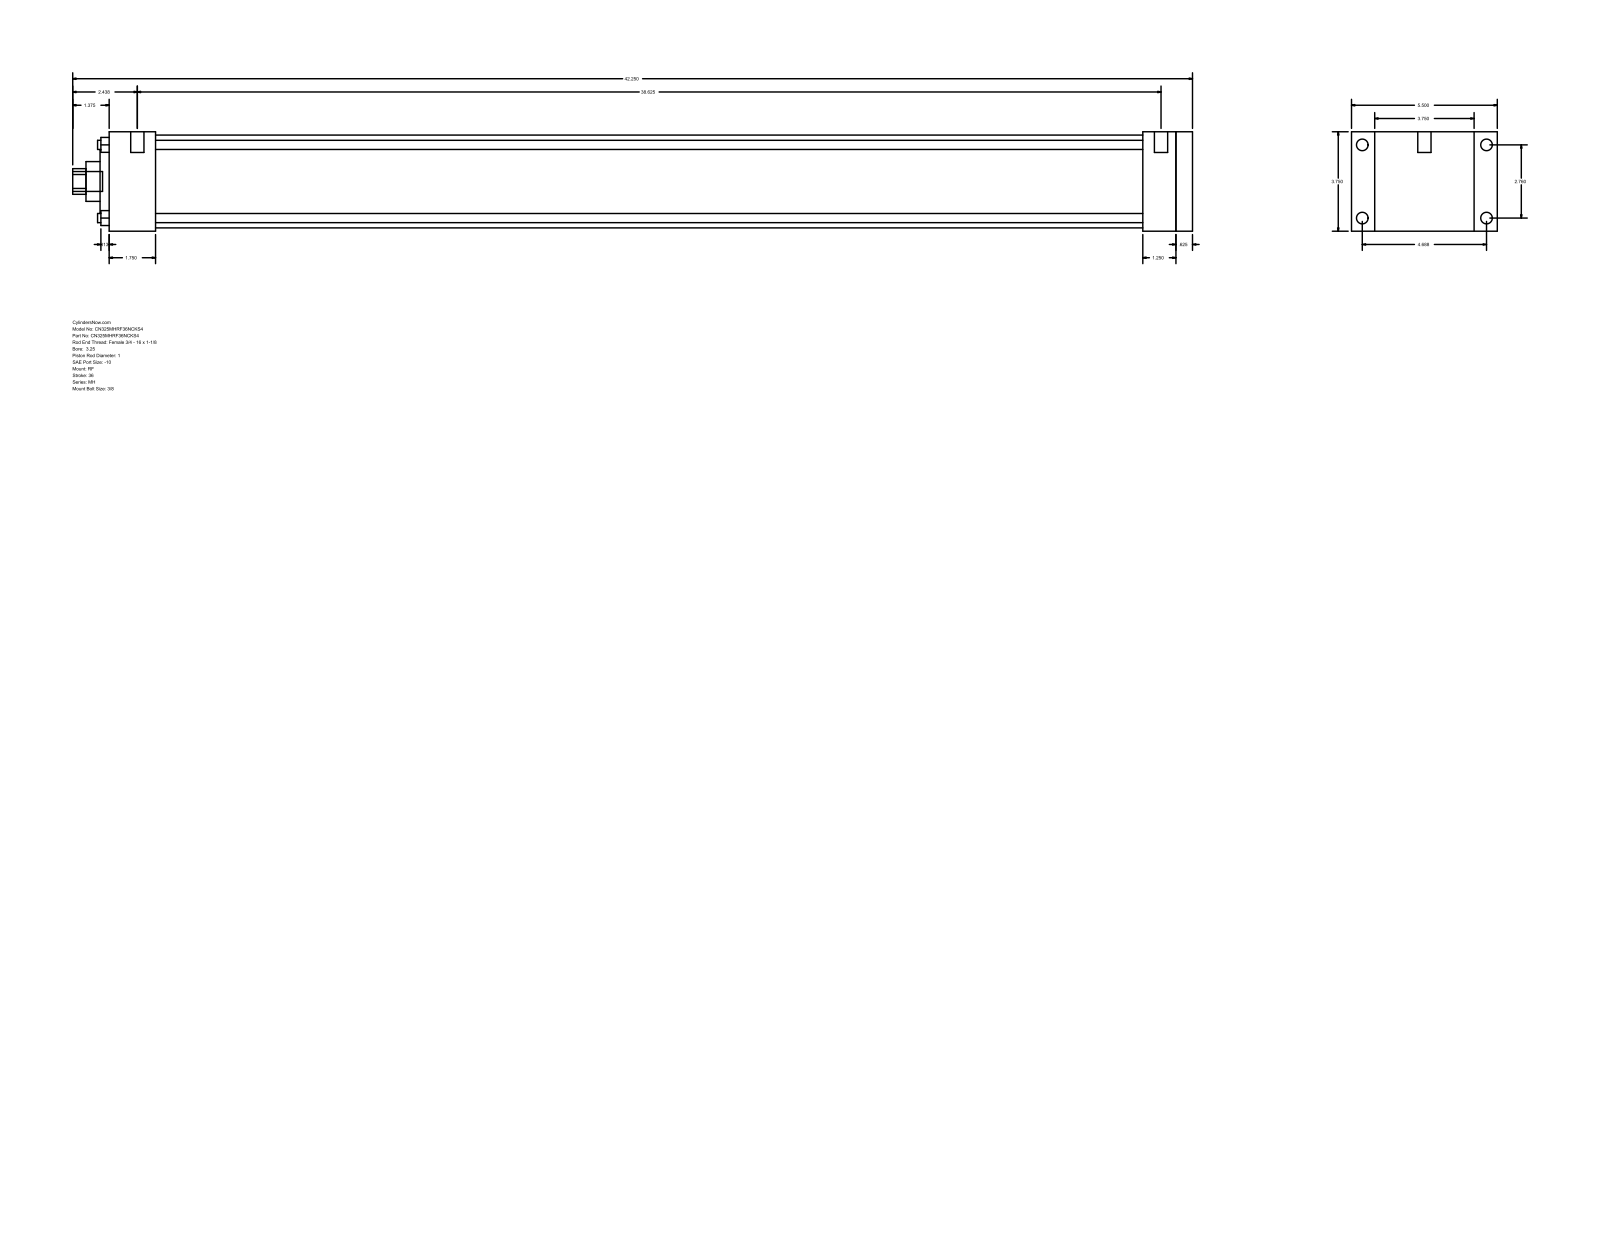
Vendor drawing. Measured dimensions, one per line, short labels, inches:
name: MH_RF__0325_1
written by: GSSL Pune (CONFIG_CONTROL_DESIGN)
unit: in
bodies: 0 solids, 94 faces (65 planar, 29 cylindrical, 0 other)
size: 42.25 × 5.5 × 3.75
holes: 4× ⌀0.345, 1× ⌀1, 1× ⌀1.5, 1× ⌀2.375, 1× ⌀3.5
bosses: 4× ⌀0.438, 4× ⌀0.219, 2× ⌀0.5, 1× ⌀0.75
rounds: 1× R0.484
face distances: 3.75, 40.875, 0.625, 40.25, 0.875, 4.625, 1.75, 38.5, 39.125, 39
hole spacings: 1.952, 2.76, 3.903
